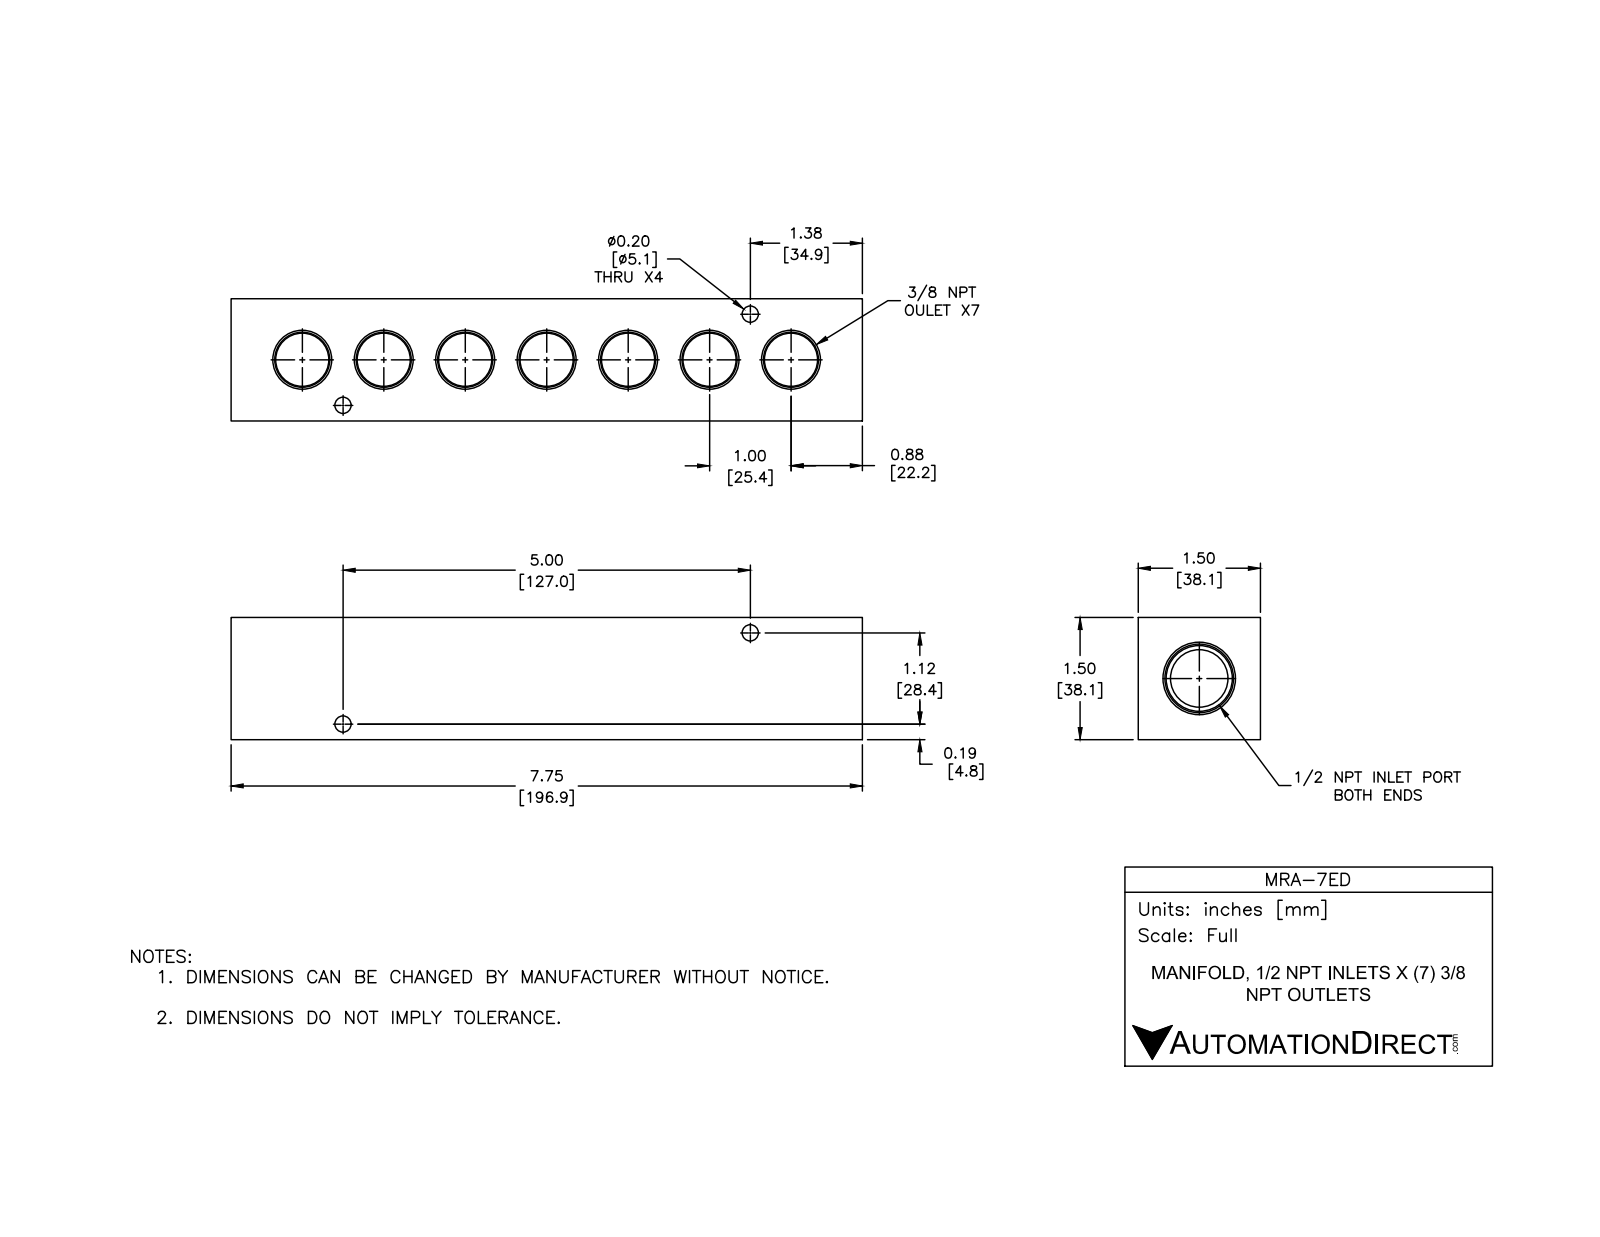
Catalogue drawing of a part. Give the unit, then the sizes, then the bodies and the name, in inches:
Units: inches
Overall size (bounding box): 7.75 × 1.5 × 1.5
Round holes (diameter × count): ⌀0.562 ×7, ⌀0.2 ×4, ⌀0.703 ×1
Main face-to-face distances: 1.5, 7.75, 1.09, 0.41, 0.53, 7.22, 6.69
Hole centre spacings: 1, 2, 0.751, 3, 4, 1.601, 2.562, 3.544
Volume: 13.06 in³ · Surface area: 73.18 in²
Bodies: 1 solid, 90 faces (22 planar, 32 cylindrical, 36 other)
Part name (STEP PRODUCT): MRA-7ED
STEP written by: SolidWorks 2015 (CONFIG_CONTROL_DESIGN)
